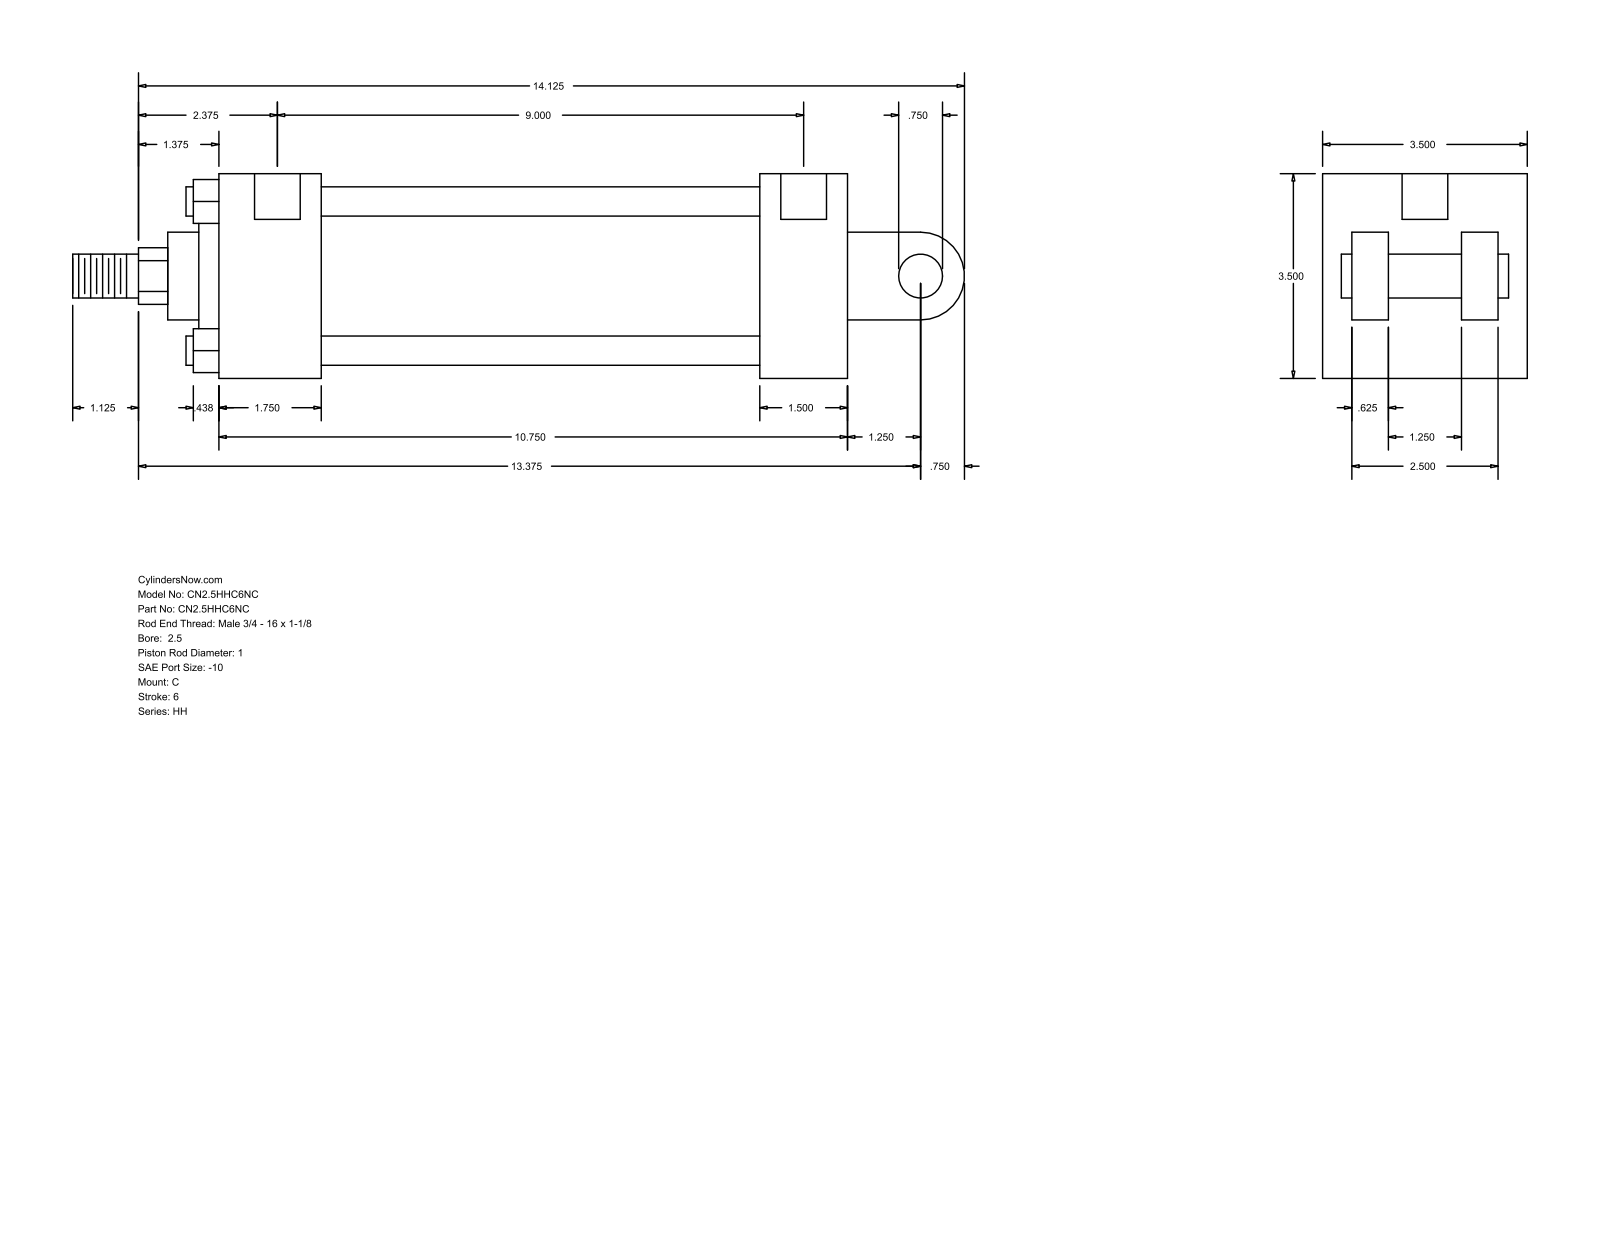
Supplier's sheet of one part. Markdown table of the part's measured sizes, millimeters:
| quantity | value |
| --- | --- |
| part name | HH_C__0250_1 |
| STEP written by | GSSL Pune (CONFIG_CONTROL_DESIGN) |
| units | millimeters |
| bodies | 0 solids, 101 faces (71 planar, 30 cylindrical, 0 other) |
| overall size | 387.35 × 88.9 × 88.9 |
| round holes (diameter × count) | 5.56 × 4, 19.84 × 2 |
| round bosses / shafts (diameter × count) | 12.7 × 4, 19.05 × 2, 73.03 × 1, 60.33 × 1, 38.1 × 1, 25.4 × 1 |
| partial cylindrical surfaces (radius × count) | 12.29 × 1, 19.05 × 1 |
| main face-to-face distances | 88.9, 38.1, 273.06, 63.5, 234.96, 44.46, 190.5, 228.6, 12.7, 28.57 |
| hole center spacings | 231.77, 1.58, 1.59, 228.6, 230.18, 230.19 |
